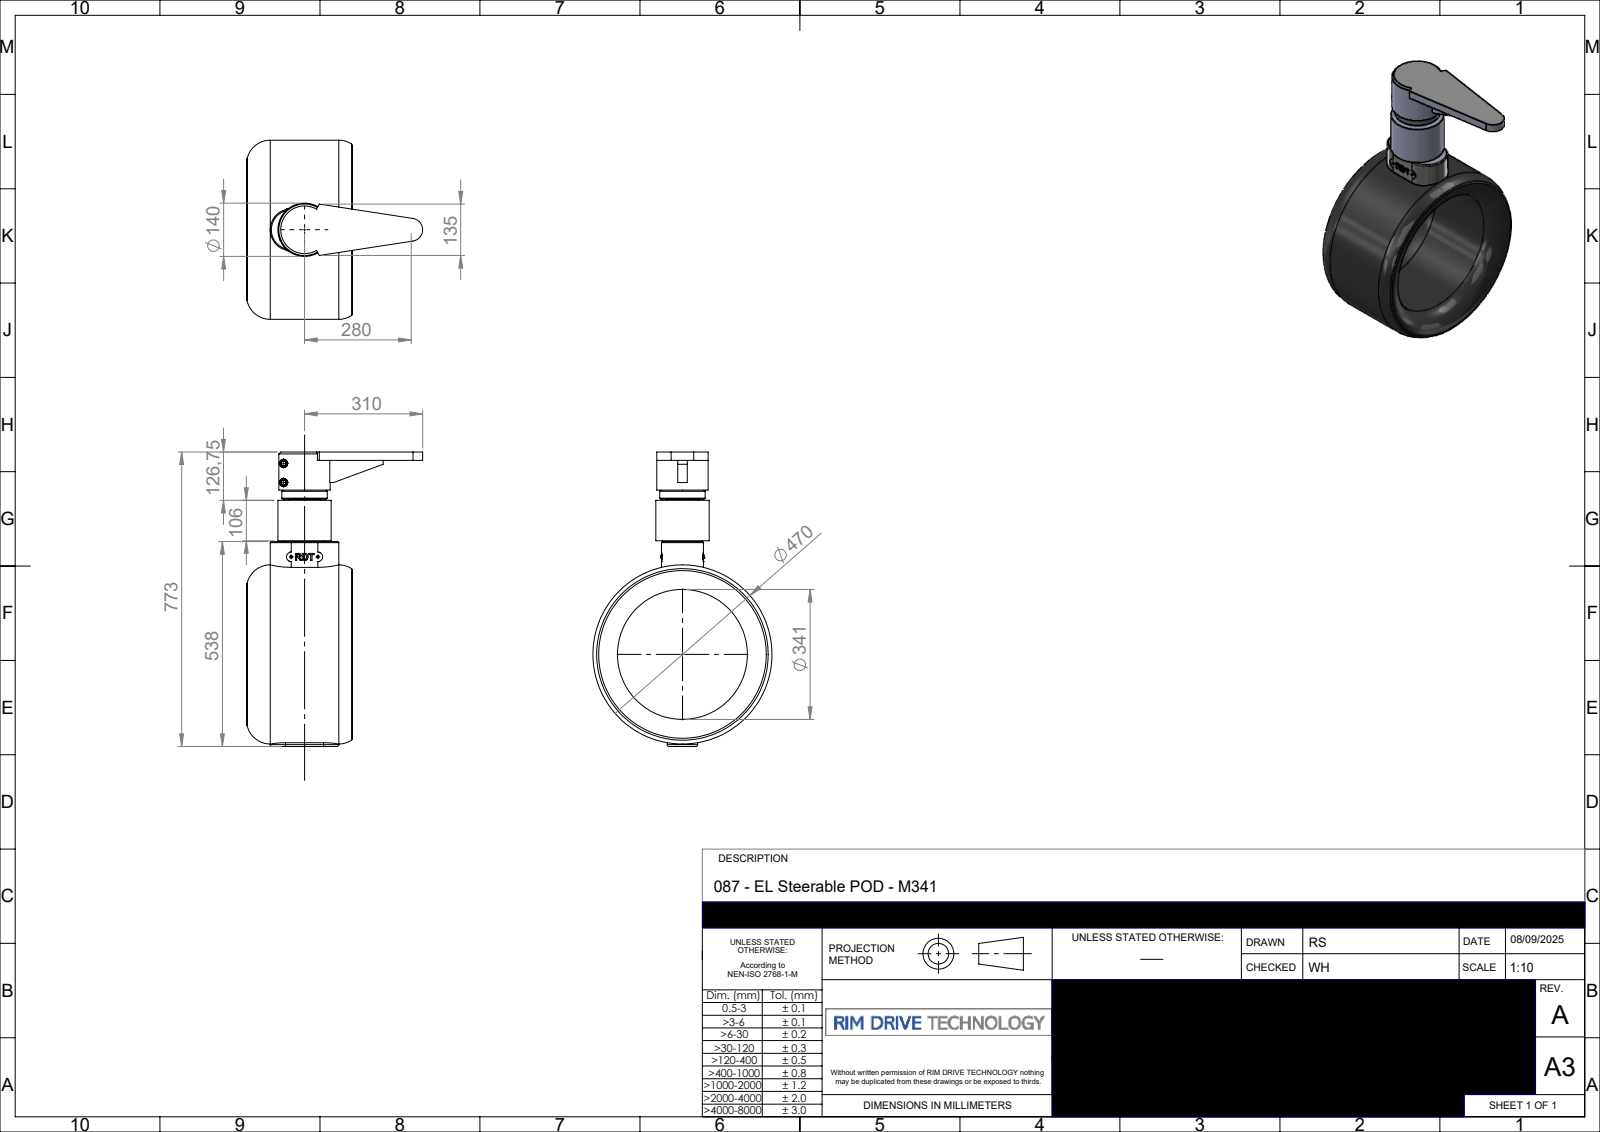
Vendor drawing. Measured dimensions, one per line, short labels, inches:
name: P-087-330-rev-A-M341
written by: SolidWorks 2024 (AUTOMOTIVE_DESIGN)
unit: in
bodies: 1 solid, 360 faces (222 planar, 51 cylindrical, 87 other)
size: 30.419 × 18.504 × 18.155
volume: 1 578 in³; area: 1 586 in²
holes: 2× ⌀0.165, 2× ⌀0.472, 2× ⌀0.866, 1× ⌀13.425
bosses: 6× ⌀0.456, 2× ⌀0.827, 2× ⌀0.299, 2× ⌀0.157, 1× ⌀18.504, 1× ⌀5.512, 1× ⌀5.315, 1× ⌀4.685
rounds: 2× R0.118, 2× R0.197, 2× R0.492, 2× R1.575, 2× R2.126, 2× R2.165, 1× R1.181
face distances: 0.866, 4.124, 4.99, 25.429, 29.553, 30.419, 2.657, 1.673, 21.167, 4.262
hole spacings: 1.969, 2.756, 7.721, 8.459, 9.681, 10.28
